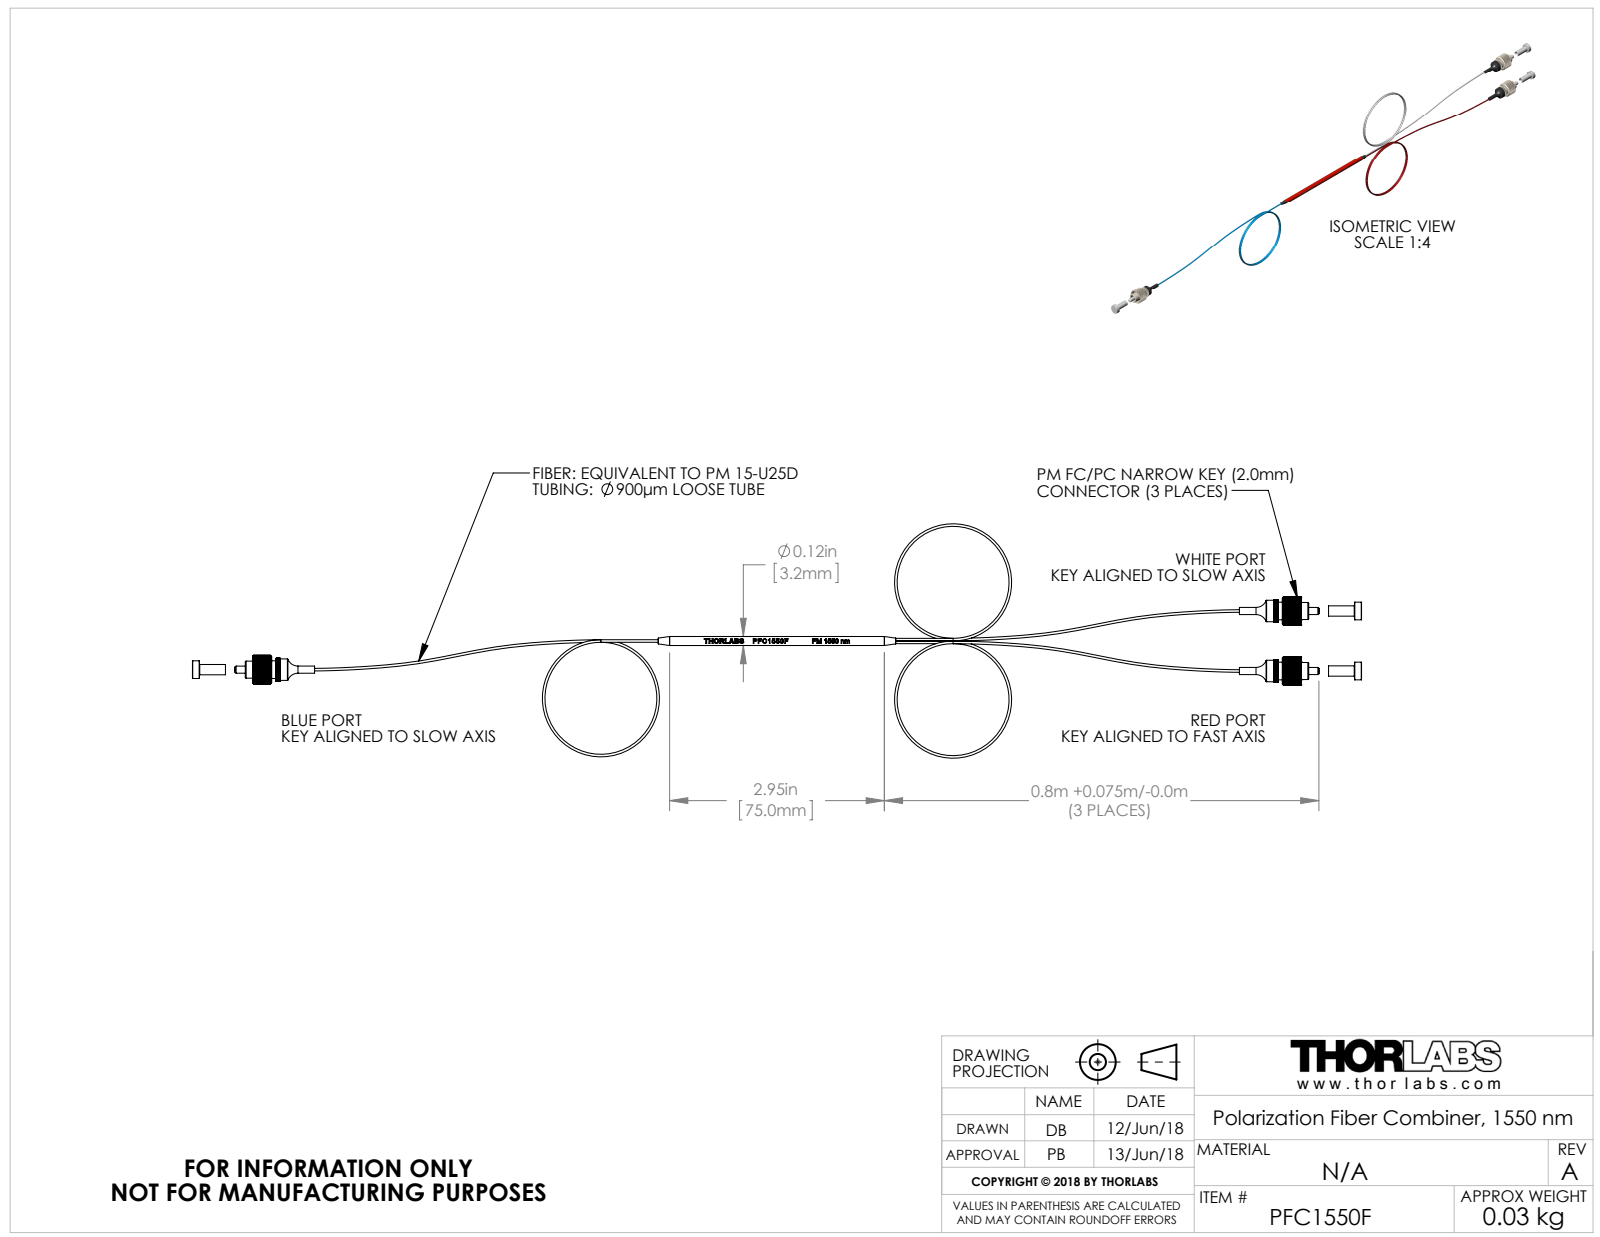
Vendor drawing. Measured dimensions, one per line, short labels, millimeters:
name: LA000PLBTTR; DWG1540; TTN157412-E0W; DWG1529 (+8 more)
written by: SolidWorks 2014 (CONFIG_CONTROL_DESIGN)
unit: mm
bodies: 32 solids, 2605 faces (1271 planar, 884 cylindrical, 450 other)
size: 408.3 × 81.85 × 14.2
volume: 3 278 mm³; area: 13 588 mm²
holes: 6× ⌀0.5, 3× ⌀0.9, 3× ⌀0.95, 3× ⌀1, 3× ⌀2.5, 3× ⌀2.8, 3× ⌀3.36, 3× ⌀4.38, 3× ⌀4.4, 3× ⌀5.08, 3× ⌀5.55, 3× ⌀6.1
bosses: 3× ⌀7.5, 3× ⌀7.07, 3× ⌀6.17, 3× ⌀6.08, 3× ⌀5.95, 3× ⌀5.38, 3× ⌀4.85, 3× ⌀3.6
rounds: 6× R0.5, 3× R0.75, 3× R1.55, 3× R2.26, 3× R3.98, 3× R5, 2× R0.45, 1× R1
face distances: 6.86, 6.85, 2, 1.43, 4.97, 2.97, 349.97, 1.54, 3.43, 27.68
hole spacings: 10.2, 0.47, 0.48, 0.95, 4.03, 9.74, 10.24, 10.66
